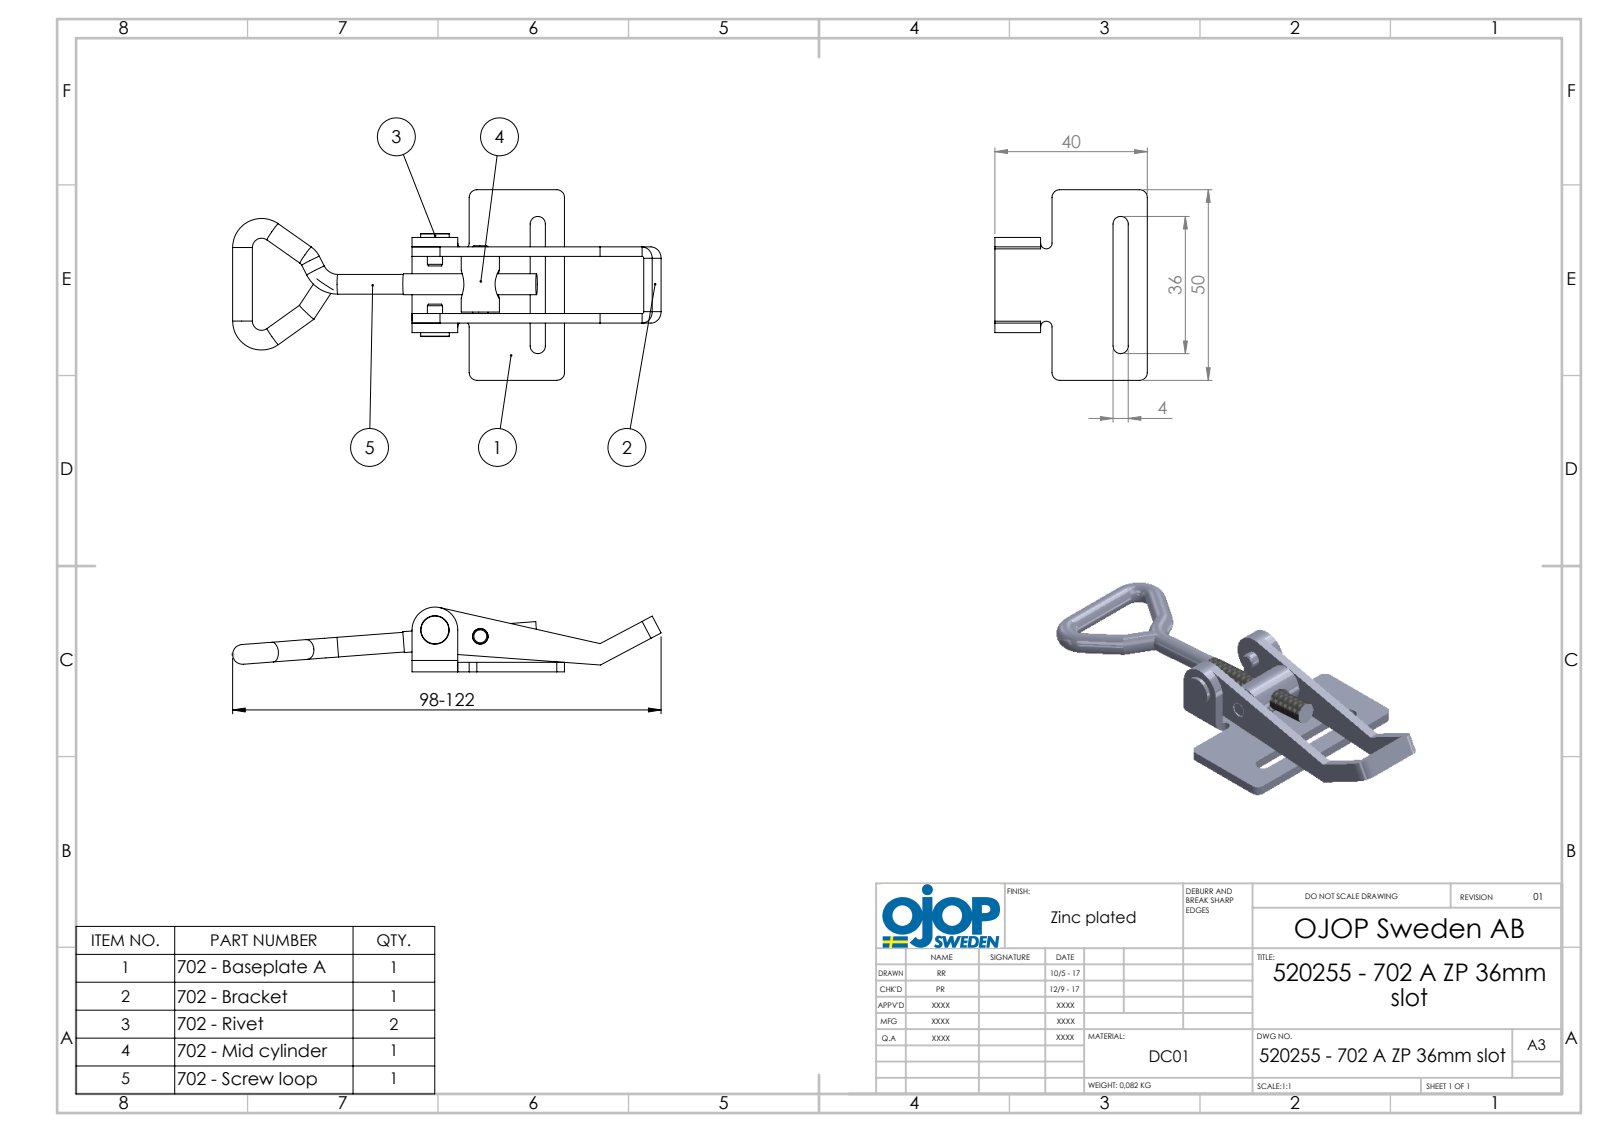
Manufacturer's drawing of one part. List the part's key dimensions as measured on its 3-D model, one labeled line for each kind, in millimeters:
Part name (STEP PRODUCT): 520255 - 702 A ZP 36mm slot; 702 - Rulle; 702 - Bygel; 702 - Skruvögla (+2 more)
STEP written by: SolidWorks 2015 (AUTOMOTIVE_DESIGN)
Units: millimetres
Bodies: 6 solids, 154 faces (59 planar, 69 cylindrical, 26 other)
Overall size (bounding box): 112.46 × 50 × 17
Volume: 11 313 mm³ · Surface area: 10 846 mm²
Round holes (diameter × count): ⌀4.1 ×2, ⌀5 ×2
Round bosses / shafts (diameter × count): ⌀5.18 ×6, ⌀4 ×2, ⌀10 ×1, ⌀7.5 ×1, ⌀6 ×1, ⌀5.5 ×1
Partial cylindrical surfaces — rounded edges, fillets, slot ends (radius × count): R2 ×6, R0.5 ×4, R3 ×4, R1.5 ×2, R6 ×1
Main face-to-face distances: 2.5, 17.5, 20, 15, 5, 22.5, 25, 35, 12.5, 32.5
Hole centre spacings: 12.03
